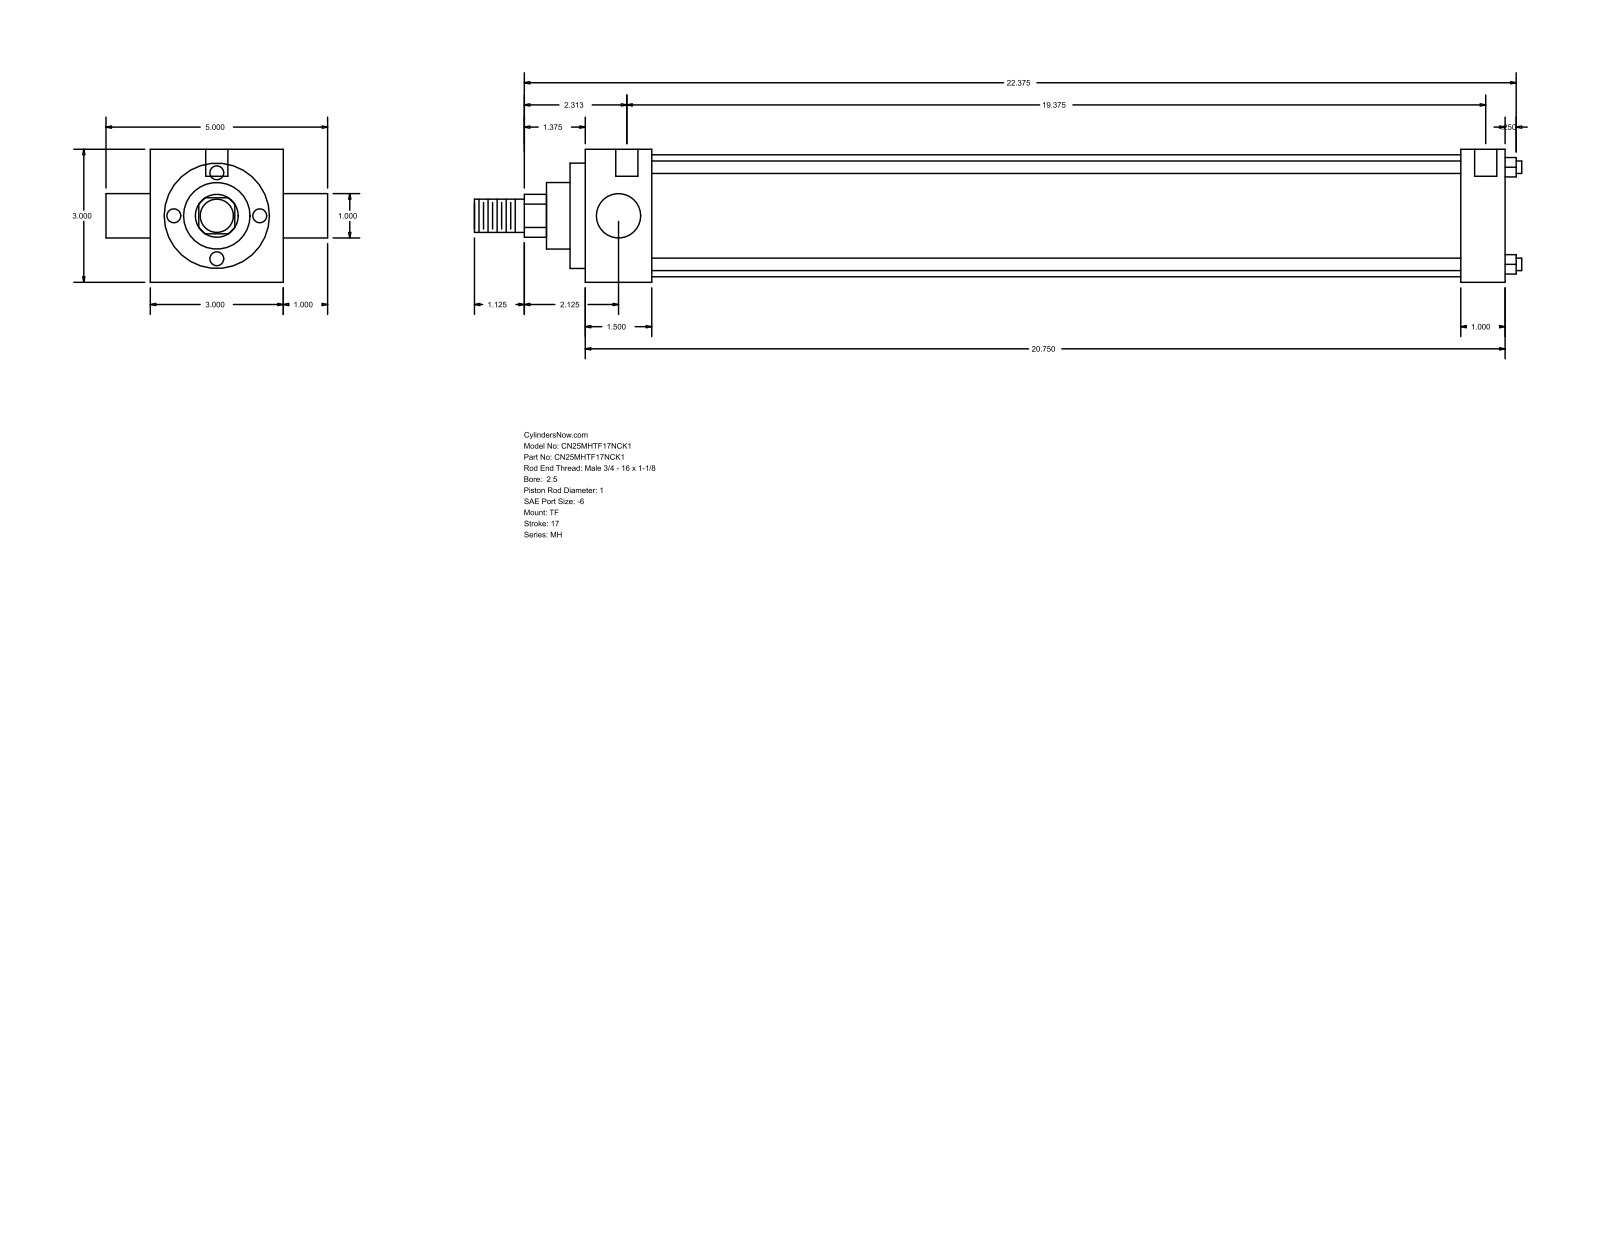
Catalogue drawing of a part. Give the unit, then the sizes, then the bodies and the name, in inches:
Units: inches
Overall size (bounding box): 23.625 × 5 × 3
Round holes (diameter × count): ⌀0.219 ×3, ⌀0.5 ×2
Round bosses / shafts (diameter × count): ⌀0.281 ×4, ⌀1 ×2, ⌀2.75 ×1, ⌀2.375 ×1, ⌀1.5 ×1, ⌀0.75 ×1
Partial cylindrical surfaces — rounded edges, fillets, slot ends (radius × count): R0.484 ×1
Main face-to-face distances: 3, 20.75, 1, 1.5, 19.25, 19.75, 18.25, 0.344, 1.844, 20.094
Hole centre spacings: 0.125, 0.187, 19.375, 19.5, 19.562, 19.687
Bodies: 0 solids, 86 faces (61 planar, 25 cylindrical, 0 other)
Part name (STEP PRODUCT): MH_TF__0250_1
STEP written by: GSSL Pune (CONFIG_CONTROL_DESIGN)
